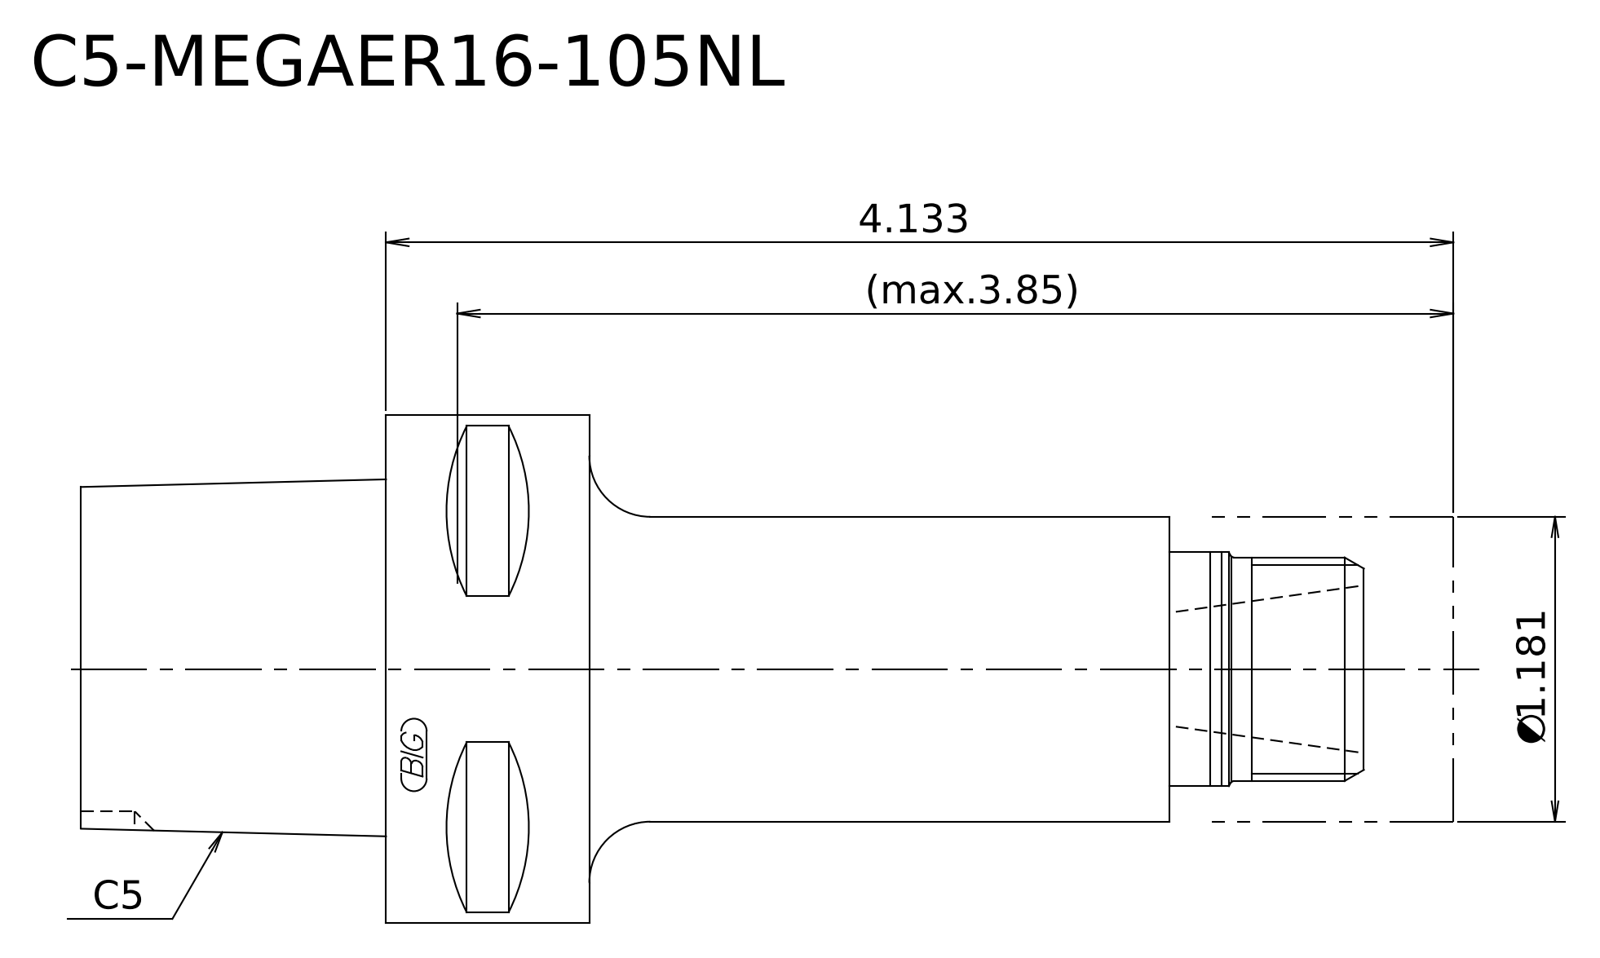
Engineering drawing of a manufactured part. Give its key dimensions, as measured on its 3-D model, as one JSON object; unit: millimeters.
{"step_written_by": "Kubotek KeyCreator 2011 V10.0.2 (22737) (automotive_design)", "units": "millimeters", "bodies": {"solids": 2, "faces": 16, "planar": 7, "cylindrical": 5, "other": 4}, "overall_size": [135, 50, 50], "volume_mm3": 133835, "surface_area_mm2": 20361, "round_bosses_or_shafts": [[50, 1], [30, 1], [23, 1], [22, 1]], "face_to_face_distances": [30, 80, 110, 25, 105, 135, 85, 60, 20, 50]}
